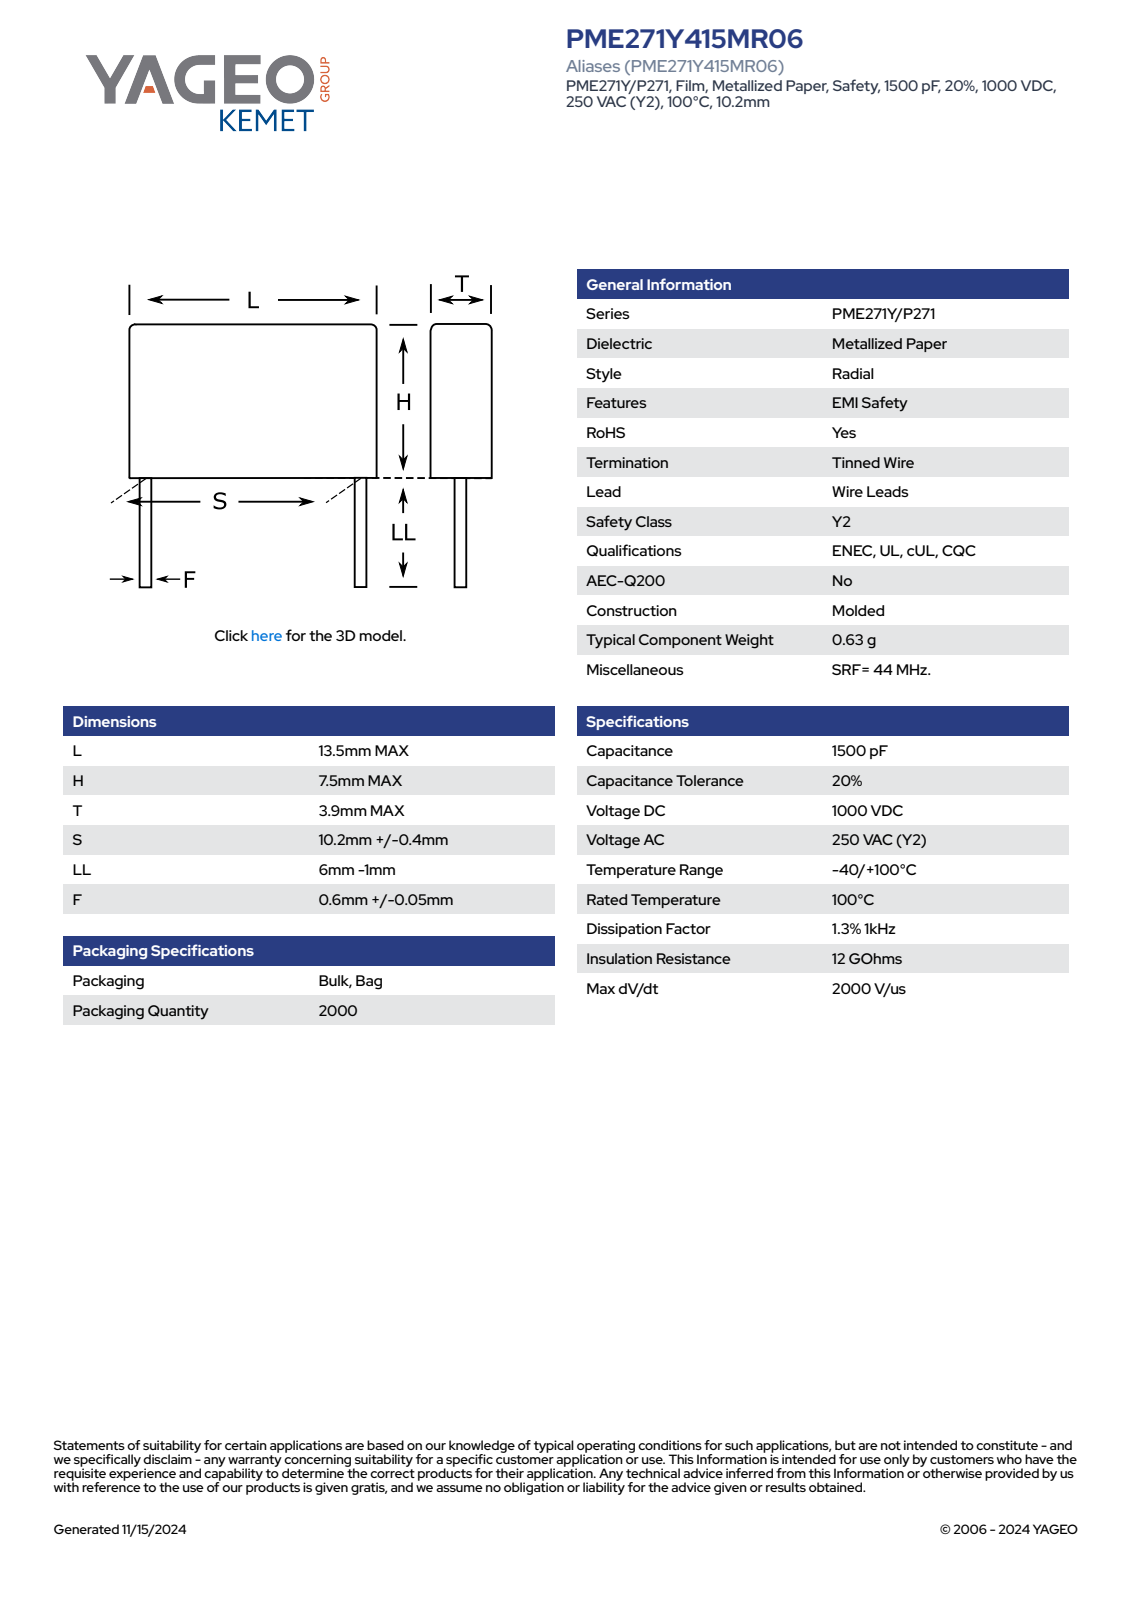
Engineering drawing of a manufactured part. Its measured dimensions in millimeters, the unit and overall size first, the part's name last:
Units: millimetres
Overall size (bounding box): 13.5 × 12.5 × 3.9
Round bosses / shafts (diameter × count): ⌀0.65 ×2
Partial cylindrical surfaces — rounded edges, fillets, slot ends (radius × count): R0.5 ×4
Main face-to-face distances: 3.9, 7.5, 13.5, 5, 12.5, 1.21, 9.35, 4.35, 3.15, 8.14
Volume: 396 mm³ · Surface area: 388 mm²
Bodies: 4 solids, 73 faces (65 planar, 8 cylindrical, 0 other)
Part name (STEP PRODUCT): CFR_MOLDED_13.5X7.5X3.9_L13.5H7.5T3.9S10.2LL5F0.65
STEP written by: SolidWorks 2014 (AUTOMOTIVE_DESIGN)
